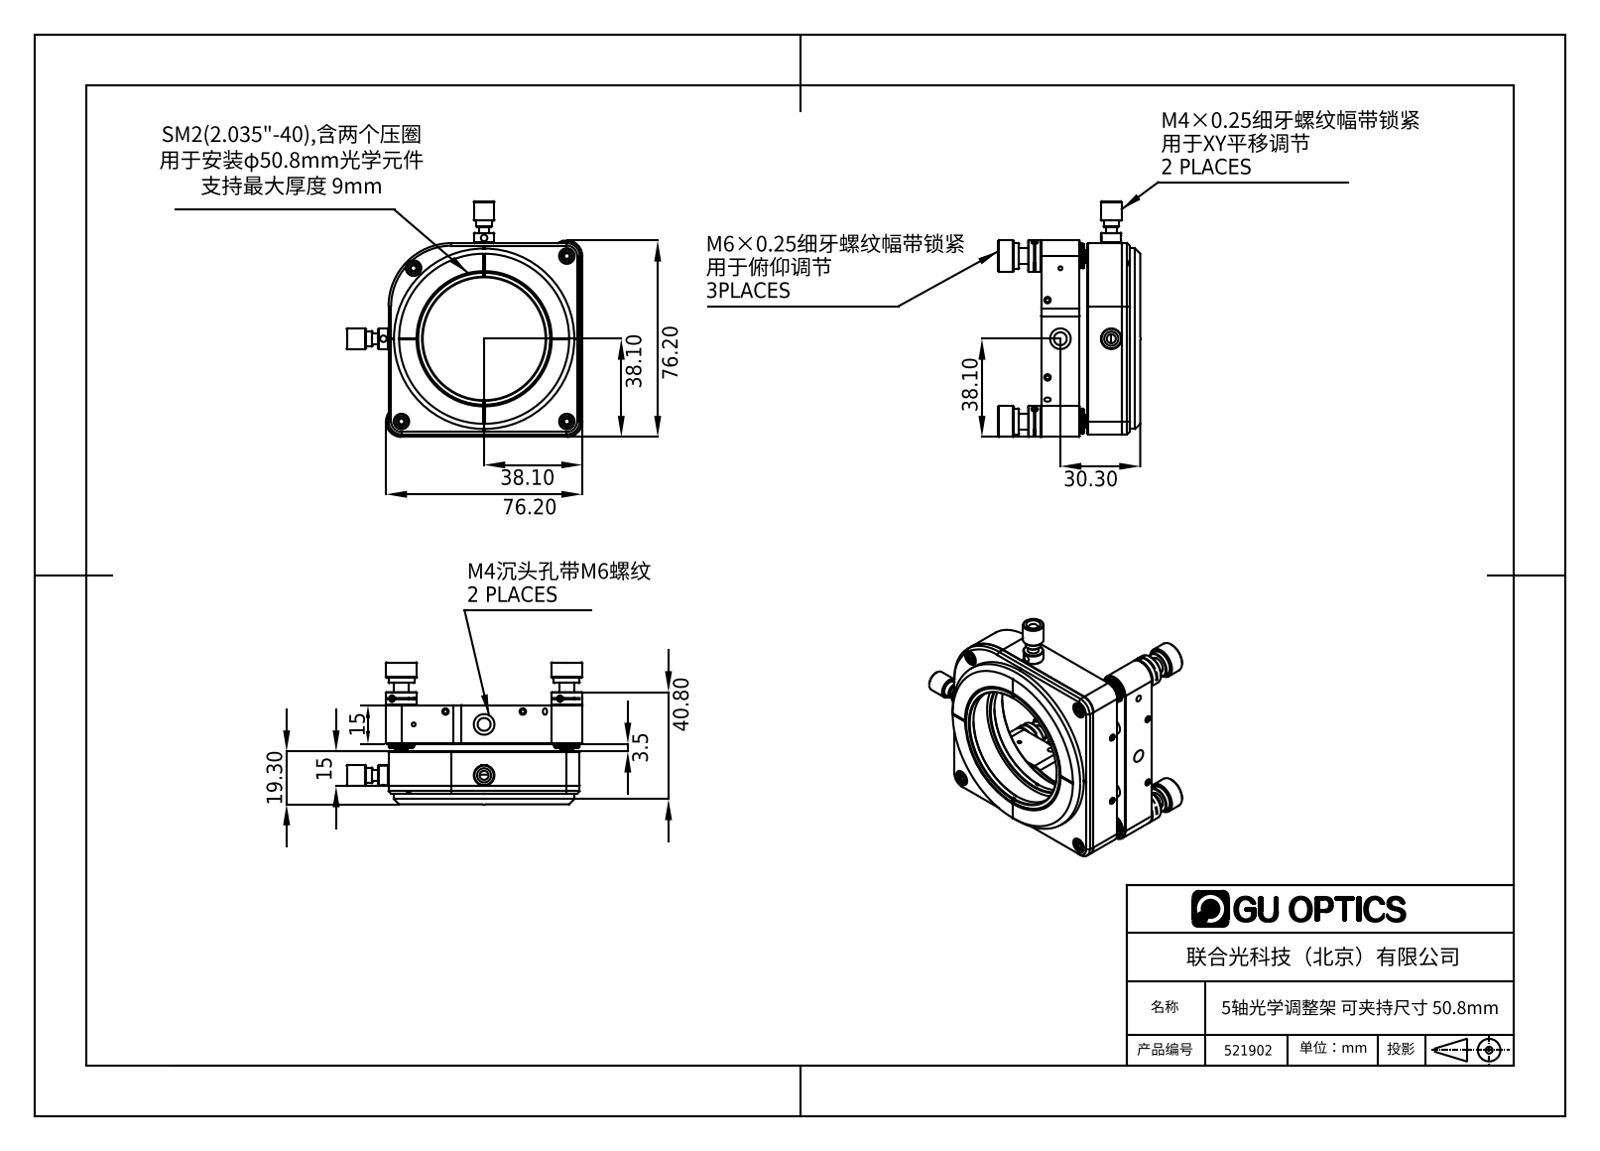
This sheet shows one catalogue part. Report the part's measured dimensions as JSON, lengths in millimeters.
{"part_name": "521902", "step_written_by": "SolidWorks 2020 (CONFIG_CONTROL_DESIGN)", "units": "millimeters", "bodies": {"solids": 0, "faces": 677, "planar": 255, "cylindrical": 222, "other": 200}, "overall_size": [91.44, 91.44, 55.07], "round_holes": [[4, 3], [8, 3], [9.5, 3], [2.5, 2], [3.5, 2], [1.8, 1], [47.69, 1], [52.5, 1]], "round_bosses_or_shafts": [[3, 10], [1.5, 10], [2.5, 7], [6, 6], [5, 5], [8, 4], [6.5, 4], [12, 3]], "partial_cylinders_radius": [[0.2, 3], [10, 2], [0.78, 1], [24.5, 1], [28, 1]], "face_to_face_distances": [7, 13.5, 1, 16.4, 2.9, 18, 20.5, 4.1, 19.4, 31.5], "hole_center_spacings": [78.1, 45.4, 32.85, 39.1, 64.2, 55.3, 90.79]}
